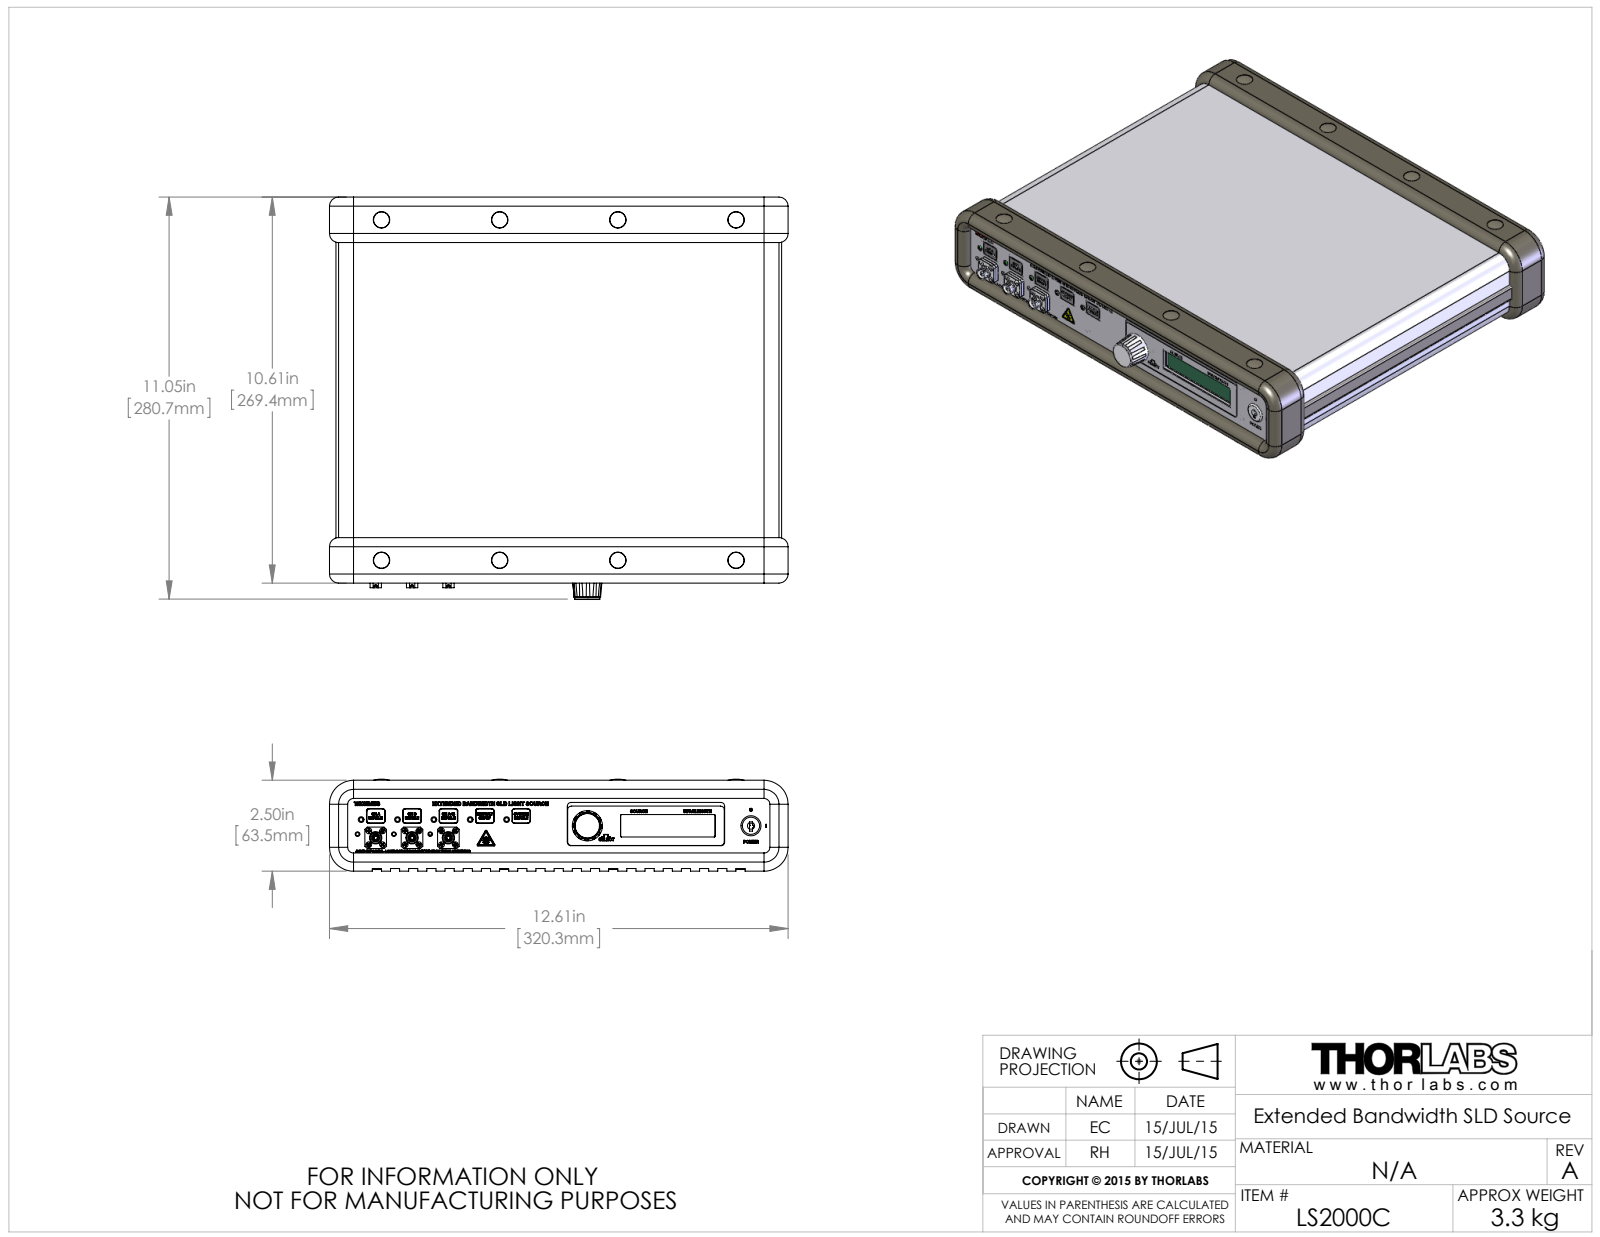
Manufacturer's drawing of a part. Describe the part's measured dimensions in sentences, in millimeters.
The part is named "TTN039382_with Justify Points; 20249-009; SunonBlower_50x50x15mm; TSW-104-15-X-D_8 Way (+8 more)". Its 3-D file was written by "SolidWorks 2014 (AUTOMOTIVE_DESIGN)". It is 179 solids with 18524 faces: 11037 planar, 4377 cylindrical and 3110 other. Overall it measures 320.3 by 280.9 by 64.3 millimeters. Its volume is 789 700 cubic millimeters and its surface area 757 400 square millimeters. Round holes: 304 of diameter 4.7, 108 of diameter 0.9, 81 of diameter 2, 38 of diameter 1.8, 30 of diameter 2.3, 30 of diameter 3.2, 18 of diameter 1, 17 of diameter 2.5, 16 of diameter 4.2, 16 of diameter 5.1, 16 of diameter 11.4, 13 of diameter 3.2. Round bosses or shafts: 28 of diameter 2.2, 28 of diameter 0.8, 16 of diameter 11, 16 of diameter 3.6, 16 of diameter 1.8, 12 of diameter 4.2, 12 of diameter 4.2, 11 of diameter 5.6. Partial cylindrical surfaces (rounded edges, fillets, slot ends): 92 of radius 0.5, 46 of radius 0.1, 35 of radius 1, 27 of radius 1.6, 20 of radius 0.3, 20 of radius 1.4, 16 of radius 0.8, 16 of radius 1. The main face-to-face distances are 1, 1.6, 8.4, 9.4, 7.9, 6.9, 255, 6.4, 254, 256. The hole center spacings are 8.5, 3.8, 8, 3.6, 5.1, 5.4, 7.6, 10.8.
